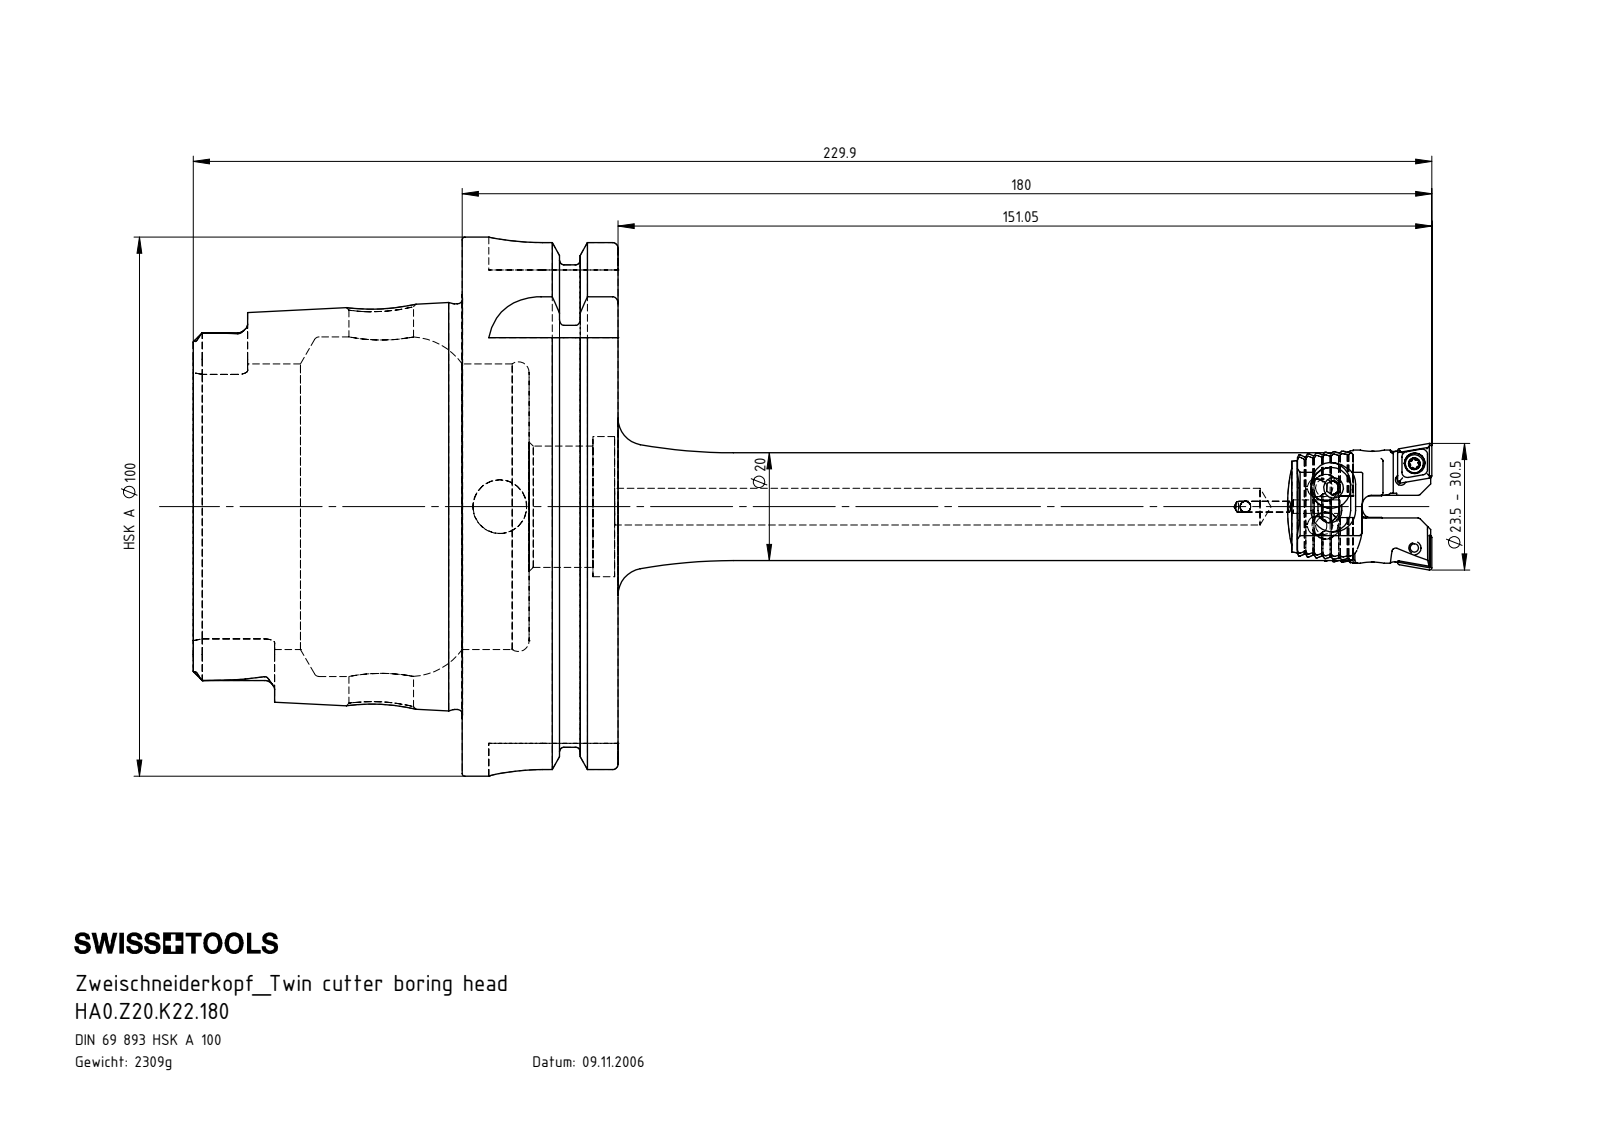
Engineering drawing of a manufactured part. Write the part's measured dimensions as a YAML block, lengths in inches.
part_name: "CCMT060204; Z20-ER1.002.008_A; Z20-WCA.001.015; Z20-ER3.001.007_A (+6 more)"
step_written_by: "SolidWorks 2022 (CONFIG_CONTROL_DESIGN)"
units: inches
bodies: {solids: 13, faces: 989, planar: 429, cylindrical: 255, other: 305}
overall_size: [9.051, 3.937, 3.937]
volume: 17.96
surface_area: 100.6
round_holes:
  - {diameter: 0.079, count: 5}
  - {diameter: 0.063, count: 2}
  - {diameter: 0.081, count: 2}
  - {diameter: 0.11, count: 2}
  - {diameter: 0.13, count: 2}
  - {diameter: 0.152, count: 2}
  - {diameter: 0.169, count: 2}
  - {diameter: 0.197, count: 2}
  - {diameter: 0.098, count: 1}
  - {diameter: 0.138, count: 1}
  - {diameter: 0.268, count: 1}
  - {diameter: 0.358, count: 1}
round_bosses_or_shafts:
  - {diameter: 0.157, count: 3}
  - {diameter: 0.299, count: 2}
  - {diameter: 0.283, count: 2}
  - {diameter: 0.134, count: 2}
  - {diameter: 0.098, count: 2}
  - {diameter: 3.937, count: 1}
  - {diameter: 3.62, count: 1}
  - {diameter: 2.963, count: 1}
partial_cylinders:
  - {radius: 0.02, count: 16}
  - {radius: 0.005, count: 14}
  - {radius: 0.005, count: 12}
  - {radius: 0.008, count: 12}
  - {radius: 0.014, count: 8}
  - {radius: 0.075, count: 6}
  - {radius: 0.394, count: 6}
  - {radius: 0.014, count: 4}
face_to_face_distances: [1.14, 0.49, 0.65, 1.965, 2.455, 3.104, 0.056, 0.026, 3.079, 1.114]
hole_center_spacings: [0.154, 0.158, 0.217, 0.518, 0.521, 0.629, 7.301, 0.39]
